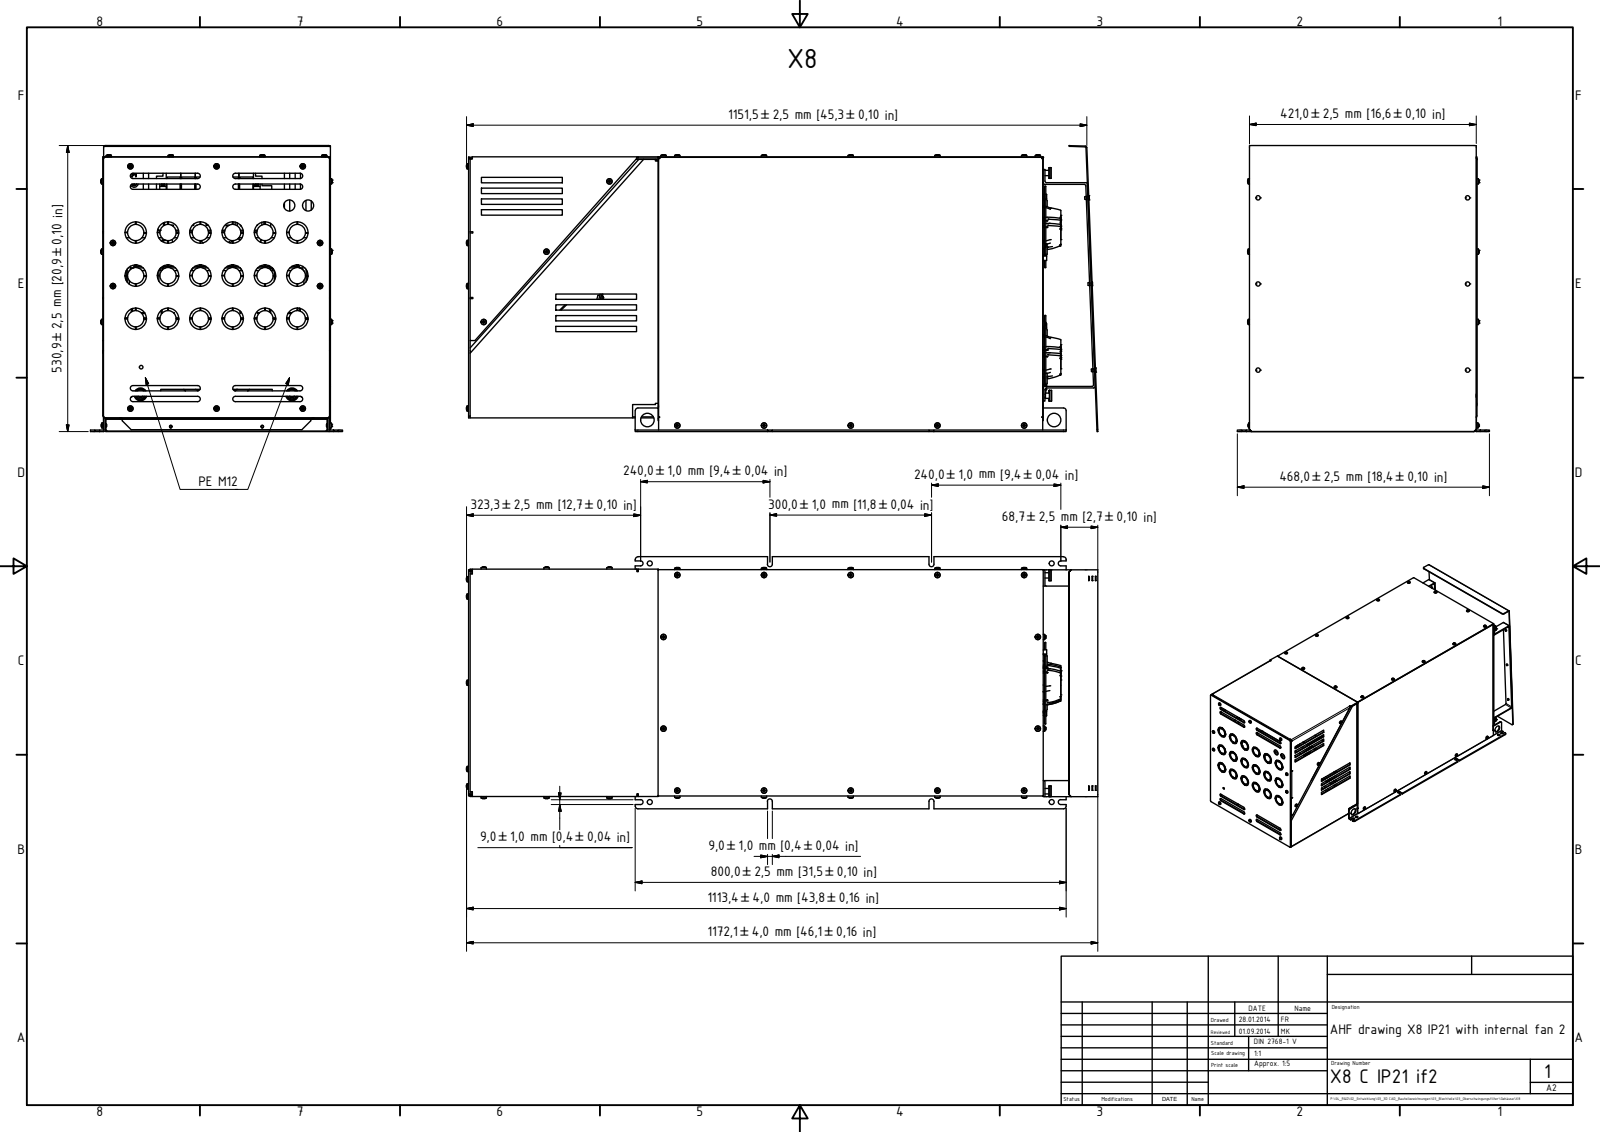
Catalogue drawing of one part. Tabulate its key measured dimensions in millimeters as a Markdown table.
| quantity | value |
| --- | --- |
| part name | 10100531 Seitenwand X8-A1; 10100530 Lüfterblech X8-A1; 10100529 Anschlussblech X8-A1; 10100404 Deckel X7-X8 (+8 more) |
| STEP written by | Autodesk Inventor 2015 (AUTOMOTIVE_DESIGN) |
| units | millimeters |
| bodies | 184 solids, 17500 faces (10337 planar, 3162 cylindrical, 4001 other) |
| overall size | 1172.06 × 530.87 × 468 |
| volume | 9 384 000 mm³ |
| surface area | 7 808 000 mm² |
| round holes (diameter × count) | 4.13 × 49, 6.5 × 47, 4 × 21, 3.24 × 20, 40 × 18, 7 × 16, 5 × 6, 9 × 6, 10 × 6, 14 × 6, 3.95 × 4, 4.25 × 4 |
| round bosses / shafts (diameter × count) | 5 × 51, 4.6 × 45, 16 × 14, 30 × 12, 26.7 × 12, 2.5 × 12, 8.5 × 10, 8 × 6 |
| partial cylindrical surfaces (radius × count) | 0.5 × 412, 0.3 × 154, 0.83 × 132, 1 × 115, 3.25 × 65, 0.31 × 64, 0.1 × 61, 2 × 57 |
| main face-to-face distances | 1, 2, 419, 420, 418, 3, 714, 421, 482.5, 1.49 |
| hole center spacings | 100, 161, 389, 7.5, 200, 400, 322, 420.62 |
